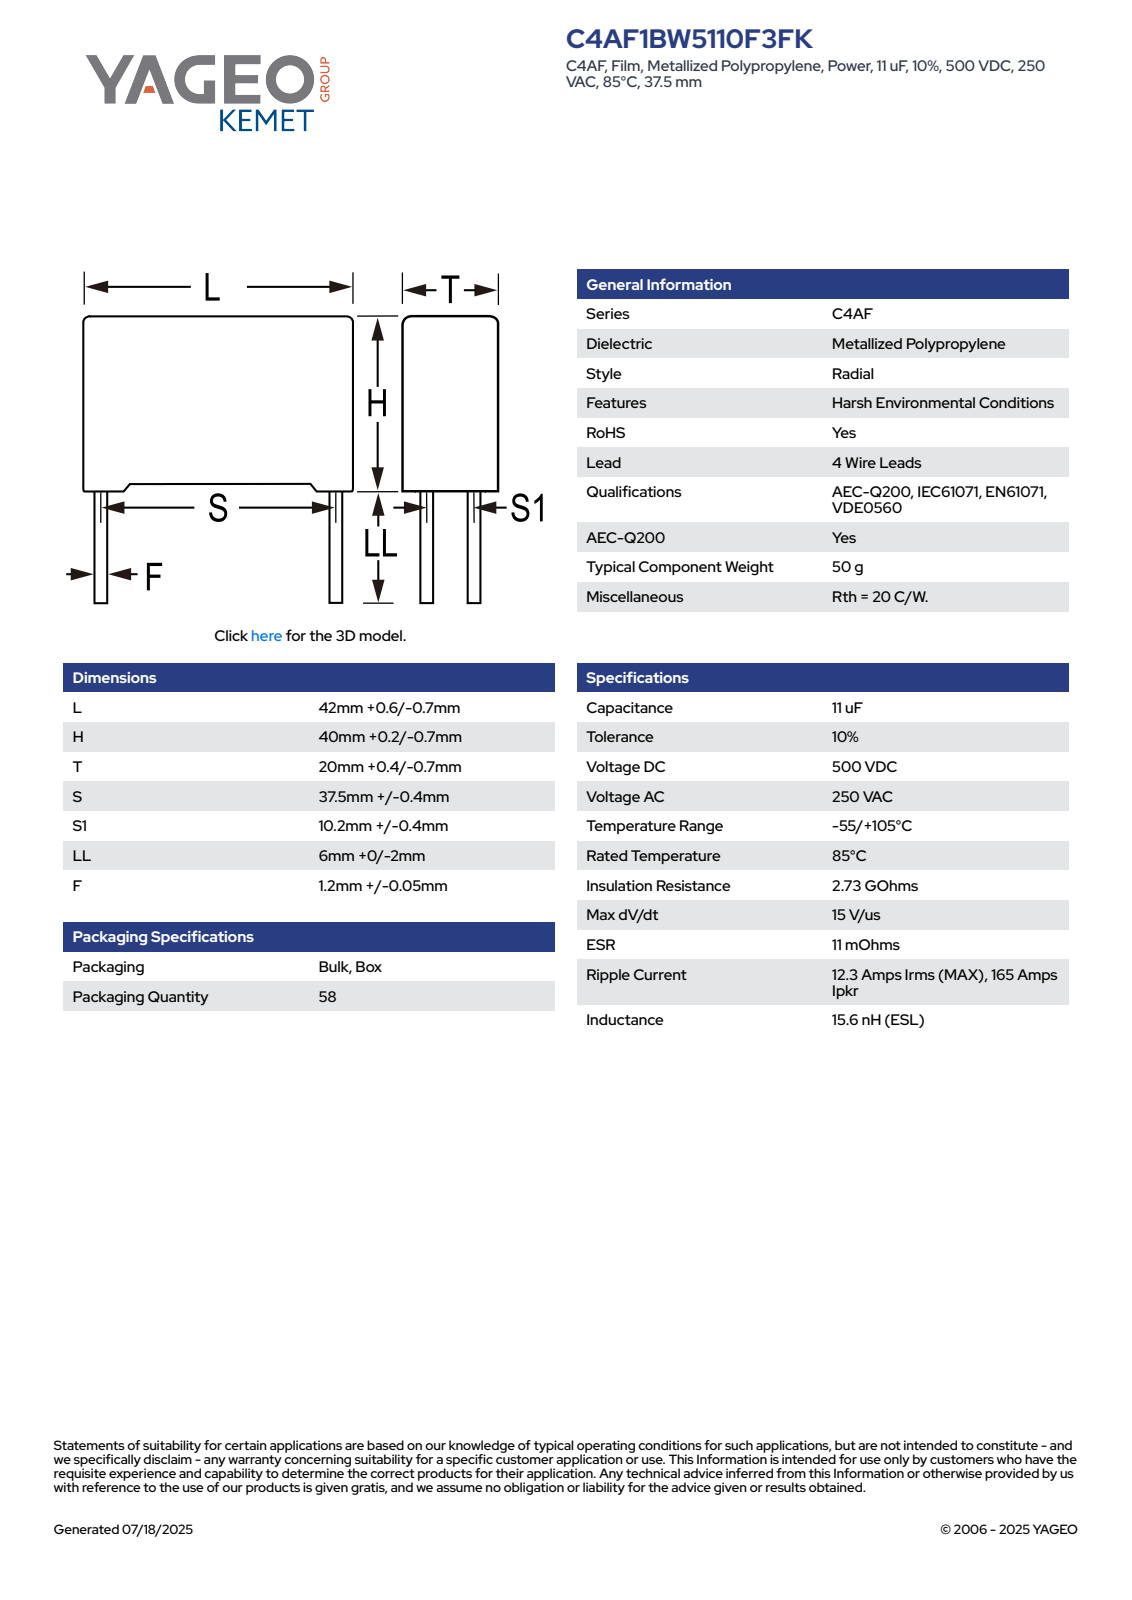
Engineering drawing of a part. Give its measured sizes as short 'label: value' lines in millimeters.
name: CFP_RB4_41.5X40X20_L42.6H40.2T20.4S37.5S110.2LL6F1.25
written by: SolidWorks 2021 (AUTOMOTIVE_DESIGN)
unit: mm
bodies: 4 solids, 87 faces (79 planar, 8 cylindrical, 0 other)
size: 46.2 × 42.6 × 20.41
volume: 34 041 mm³; area: 7 042 mm²
bosses: 4× ⌀1.25
face distances: 20.4, 42.6, 39.02, 1.18, 40.2, 1.25, 20.41, 41.35, 19.15, 40.1
